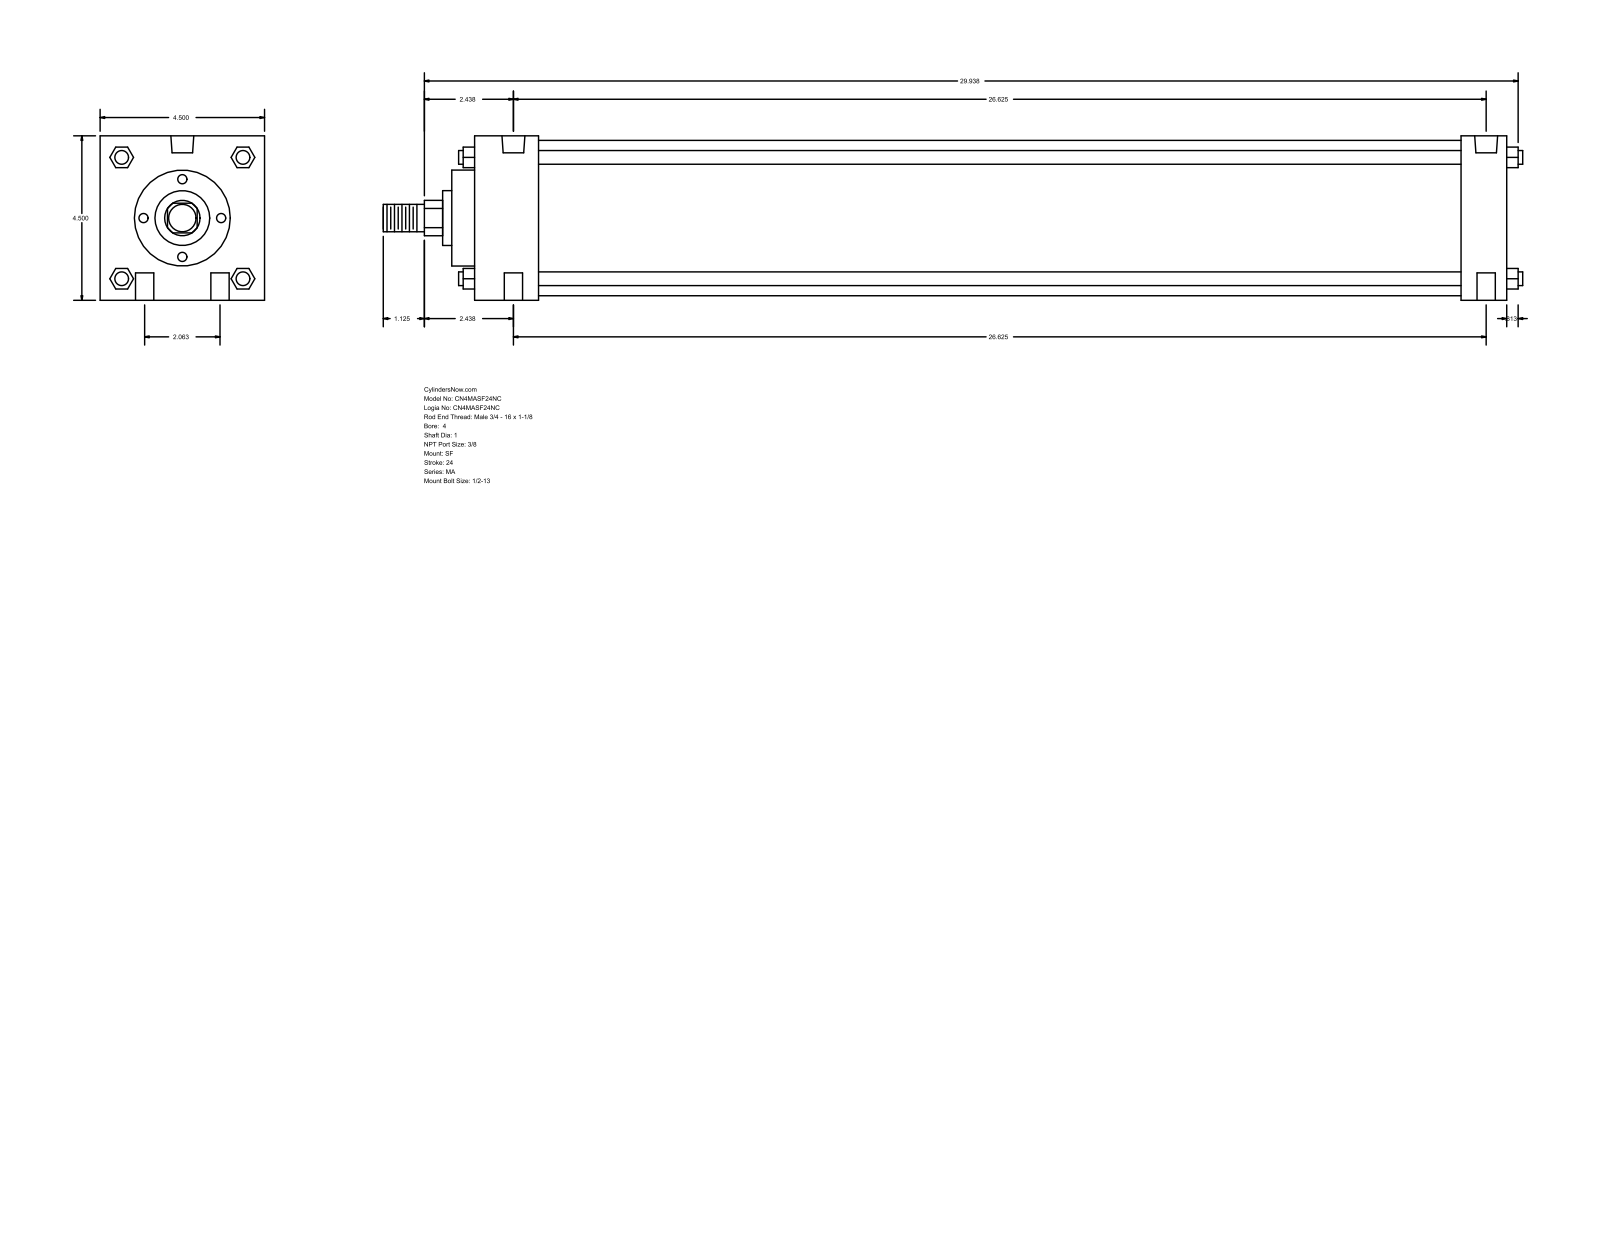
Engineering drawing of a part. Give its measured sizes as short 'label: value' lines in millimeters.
name: MA_SF__0400_1
written by: GSSL Pune (CONFIG_CONTROL_DESIGN)
unit: mm
bodies: 0 solids, 126 faces (95 planar, 31 cylindrical, 0 other)
size: 792.16 × 114.3 × 114.3
holes: 4× ⌀12.7, 2× ⌀11.11, 2× ⌀15.93
bosses: 4× ⌀9.53, 1× ⌀107.95, 1× ⌀66.67, 1× ⌀38.1, 1× ⌀25.4, 1× ⌀19.05
rounds: 1× R12.29
face distances: 114.3, 717.56, 685.81, 31.75, 44.46, 641.35, 673.1, 15.87, 60.33, 701.68
hole spacings: 26.19, 676.79, 676.28, 52.38, 678.31, 666.75
